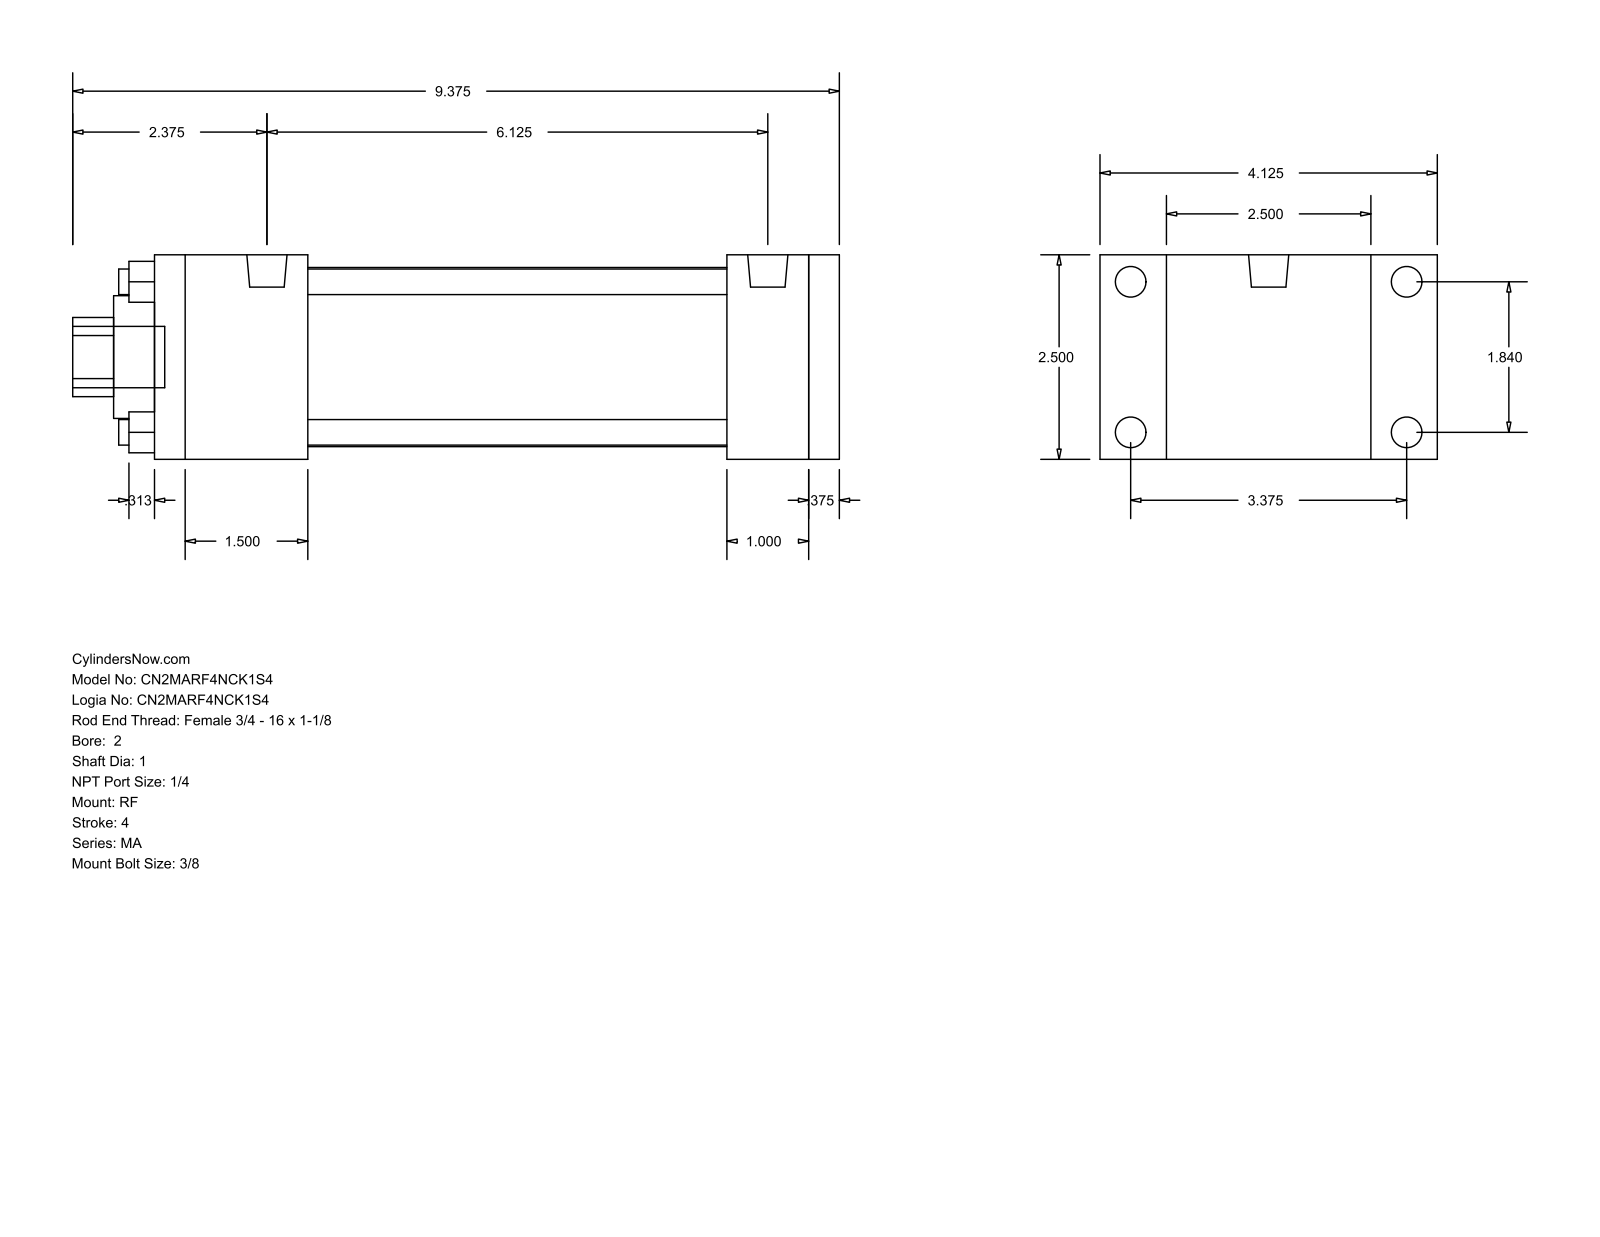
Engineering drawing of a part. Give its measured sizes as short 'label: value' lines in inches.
name: MA_RF__0200_1
written by: GSSL Pune (CONFIG_CONTROL_DESIGN)
unit: in
bodies: 0 solids, 92 faces (64 planar, 28 cylindrical, 0 other)
size: 9.375 × 4.125 × 2.5
holes: 4× ⌀0.313, 1× ⌀1, 1× ⌀1.5, 1× ⌀2.19
bosses: 4× ⌀0.375, 4× ⌀0.313, 2× ⌀0.492, 1× ⌀0.75
rounds: 1× R0.484
face distances: 2.5, 8, 0.375, 8.375, 1, 0.813, 0.5, 1.875, 6.125, 6.5
hole spacings: 1.301, 1.84, 2.602
